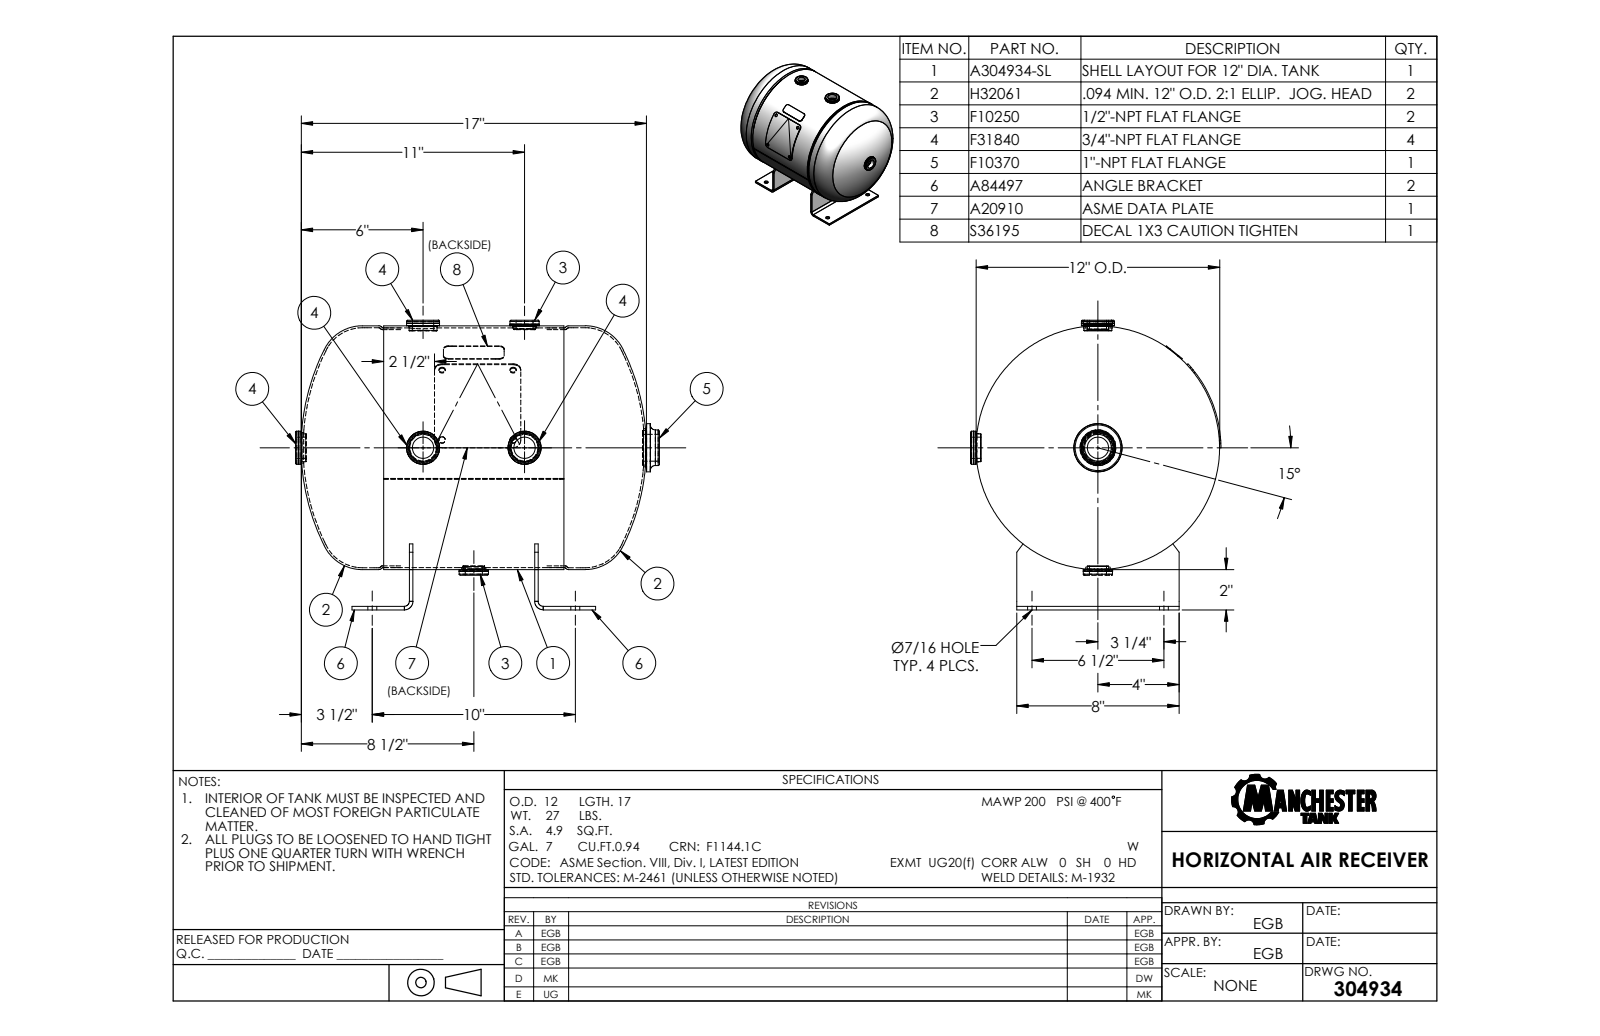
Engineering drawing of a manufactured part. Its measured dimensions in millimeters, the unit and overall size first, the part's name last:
Units: millimetres
Overall size (bounding box): 485.4 × 377 × 327.8
Round holes (diameter × count): ⌀11.1 ×4
Round bosses / shafts (diameter × count): ⌀41.4 ×4, ⌀26.7 ×4, ⌀41.3 ×3, ⌀36.8 ×2, ⌀36.5 ×2, ⌀21.3 ×2, ⌀304.8 ×1, ⌀299.7 ×1
Partial cylindrical surfaces — rounded edges, fillets, slot ends (radius × count): R6.4 ×6, R10.9 ×2, R153.9 ×1
Main face-to-face distances: 4.5, 156.9, 152.4, 161.5, 32, 36.5, 188.9, 193.5, 225.4, 3.2
Hole centre spacings: 165.1, 254, 302.9
Bodies: 0 solids, 261 faces (115 planar, 70 cylindrical, 76 other)
Part name (STEP PRODUCT): 304934
STEP written by: SolidWorks 2012 (CONFIG_CONTROL_DESIGN)
